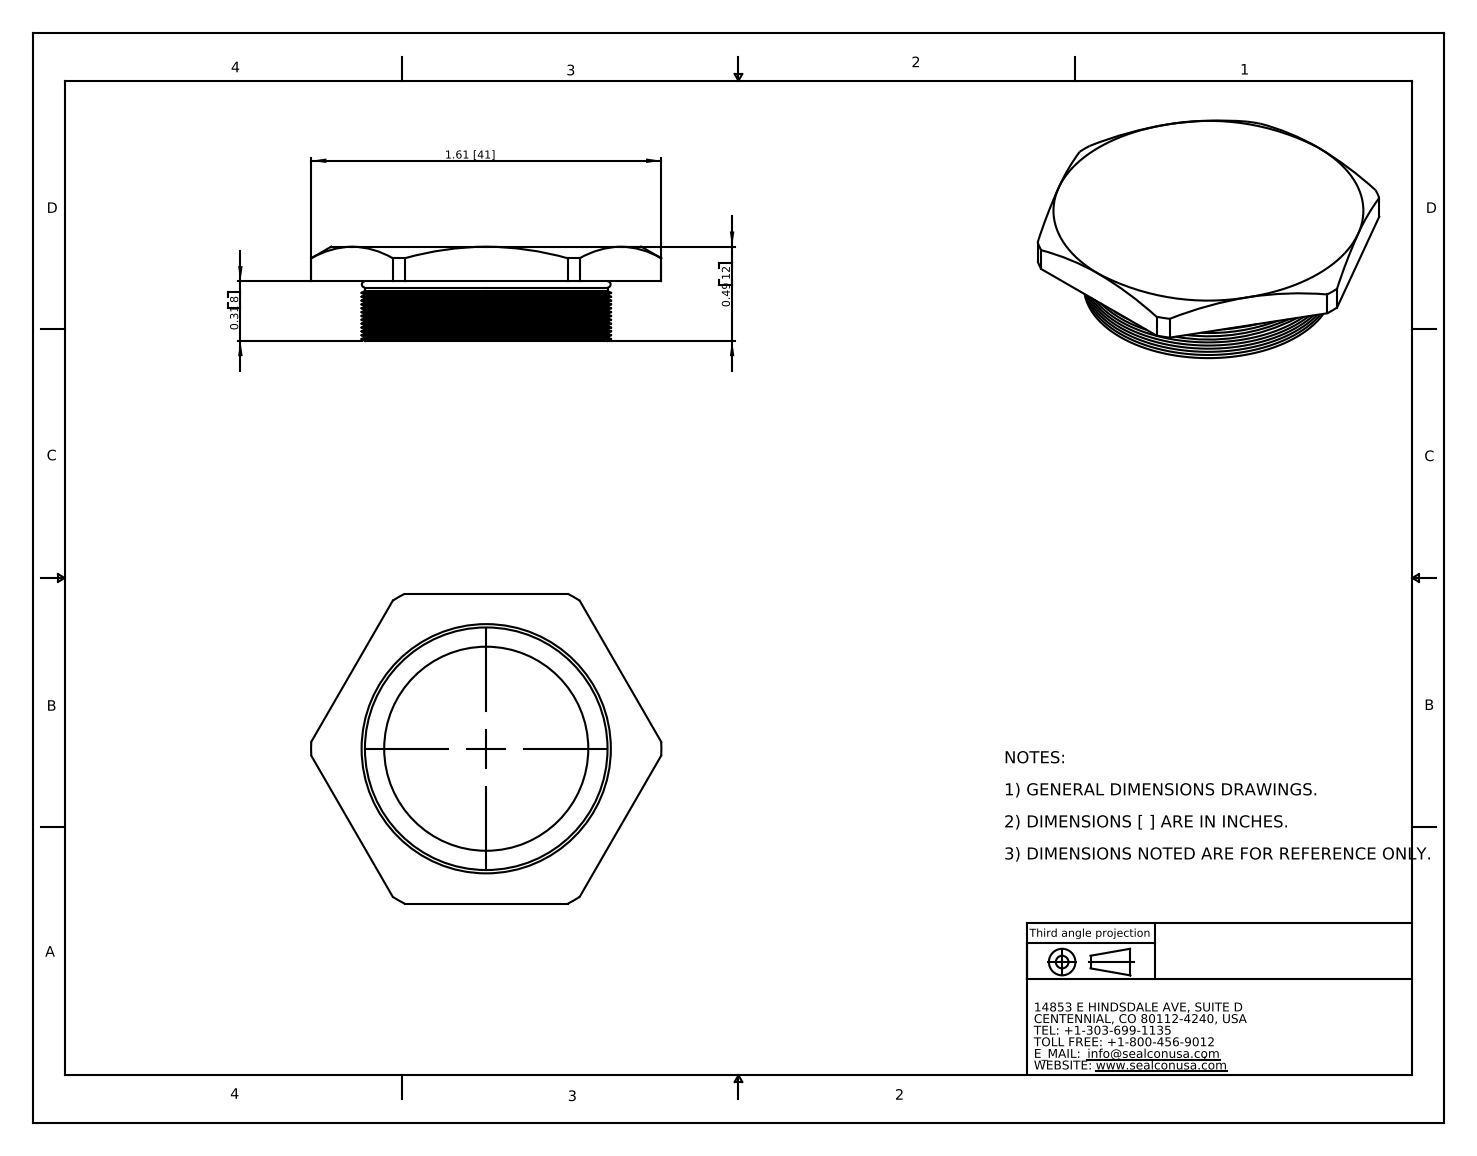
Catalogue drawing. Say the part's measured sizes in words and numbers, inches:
The part is named "HM-32-SS-V". Its 3-D file was written by "SolidWorks 2007 (CONFIG_CONTROL_DESIGN)". It is 1 solid with 80 faces: 10 planar, 10 cylindrical and 60 other. Overall it measures 1.819 by 1.61 by 0.49 inches. Its volume is 0.523 cubic inches and its surface area 8.767 square inches. Round holes: 1 of diameter 1.06. Round bosses or shafts: 1 of diameter 1.26. Partial cylindrical surfaces (rounded edges, fillets, slot ends): 1 of radius 0.91. The main face-to-face distances are 0.18, 1.61, 0.31, 0.49.
